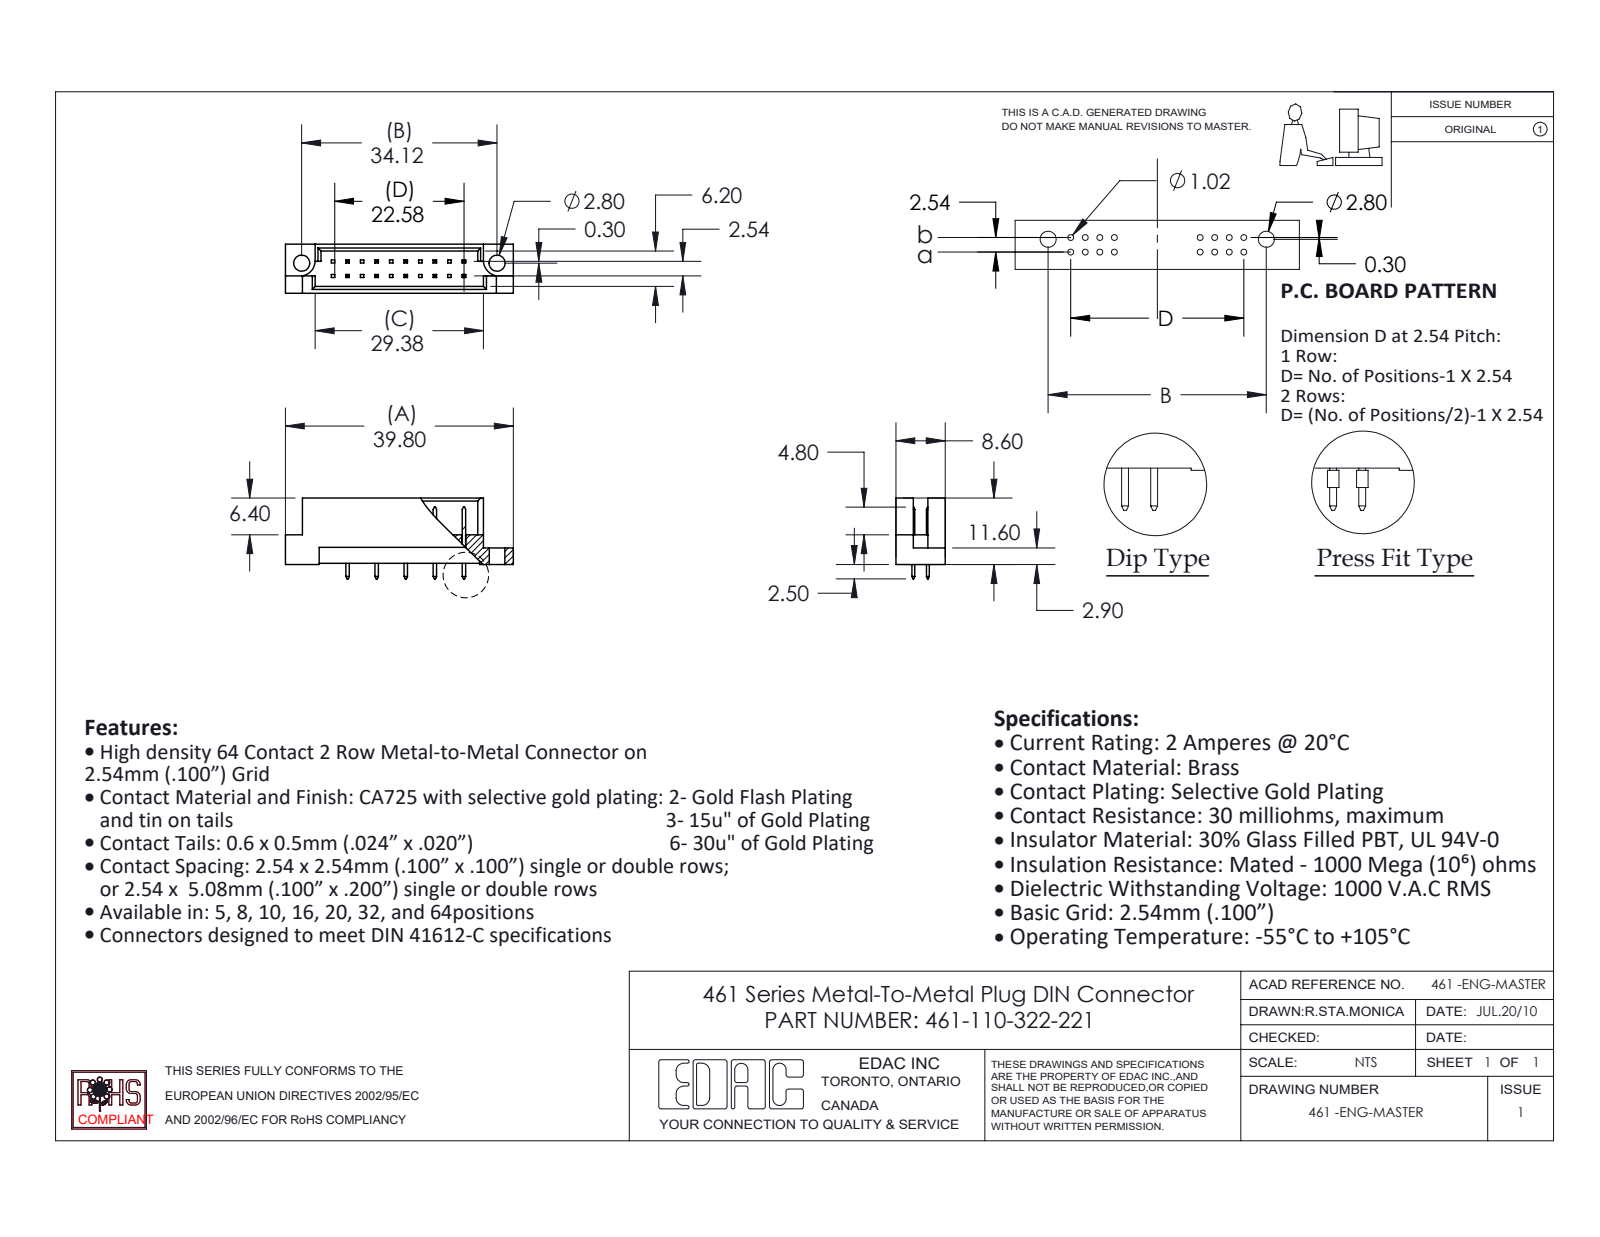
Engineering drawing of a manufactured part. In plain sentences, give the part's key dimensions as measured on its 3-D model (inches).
The part is named "461 Part_20; 461-290_22; 461-110-322-221". Its 3-D file was written by "SolidWorks 2020 (CONFIG_CONTROL_DESIGN)". It is 11 solids with 268 faces: 262 planar, 6 cylindrical and 0 other. Overall it measures 1.567 by 0.555 by 0.339 inches. Its volume is 0.118 cubic inches and its surface area 4.044 square inches. Round holes: 2 of diameter 0.11. Partial cylindrical surfaces (rounded edges, fillets, slot ends): 2 of radius 0.11. The main face-to-face distances are 0.047, 0.291, 0.339, 0.244, 0.197, 0.1, 0.2, 0.129, 0.209, 0.082. The hole center spacings are 1.343.
